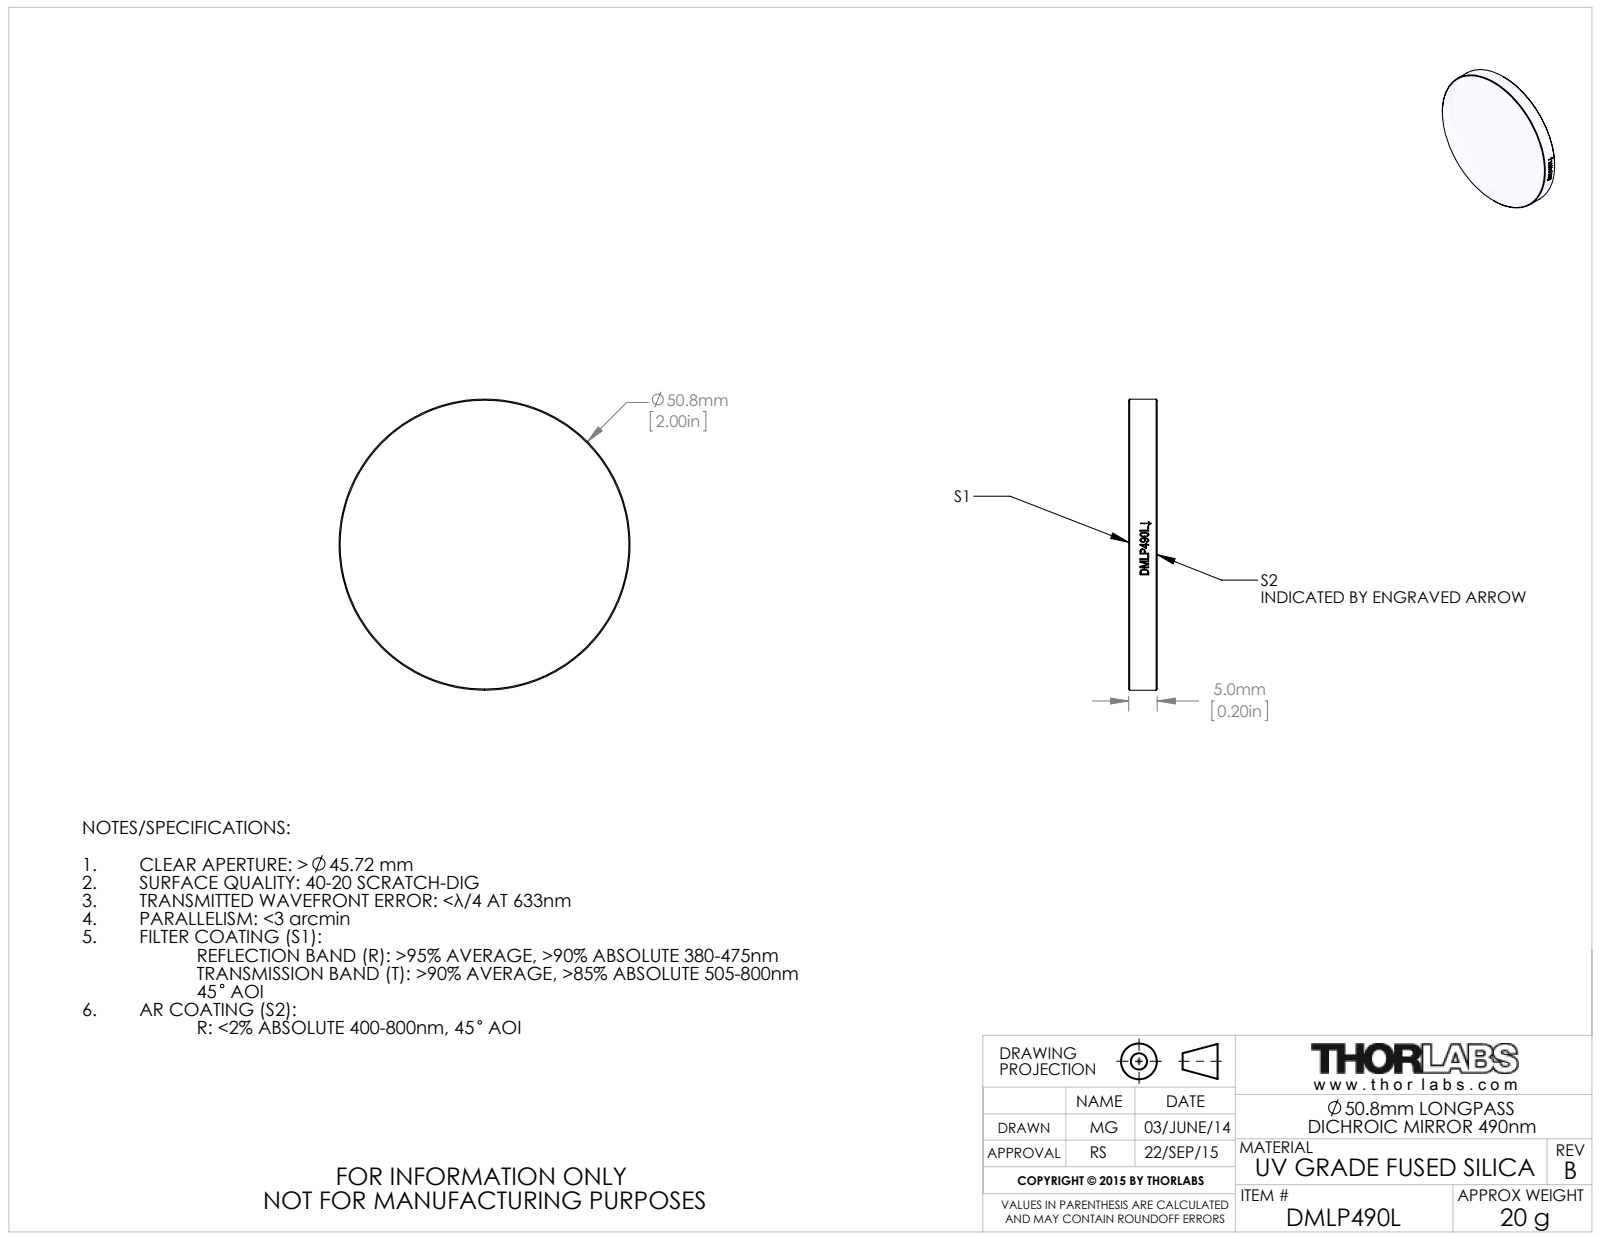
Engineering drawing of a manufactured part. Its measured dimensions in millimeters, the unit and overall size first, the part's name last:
Units: millimetres
Overall size (bounding box): 50.8 × 50.8 × 5
Round bosses / shafts (diameter × count): ⌀50.8 ×1
Main face-to-face distances: 5
Volume: 10 128 mm³ · Surface area: 4 814 mm²
Bodies: 1 solid, 22 faces (2 planar, 16 cylindrical, 4 other)
Part name (STEP PRODUCT): TTN028306-E0W
STEP written by: SolidWorks 2012 (CONFIG_CONTROL_DESIGN)
